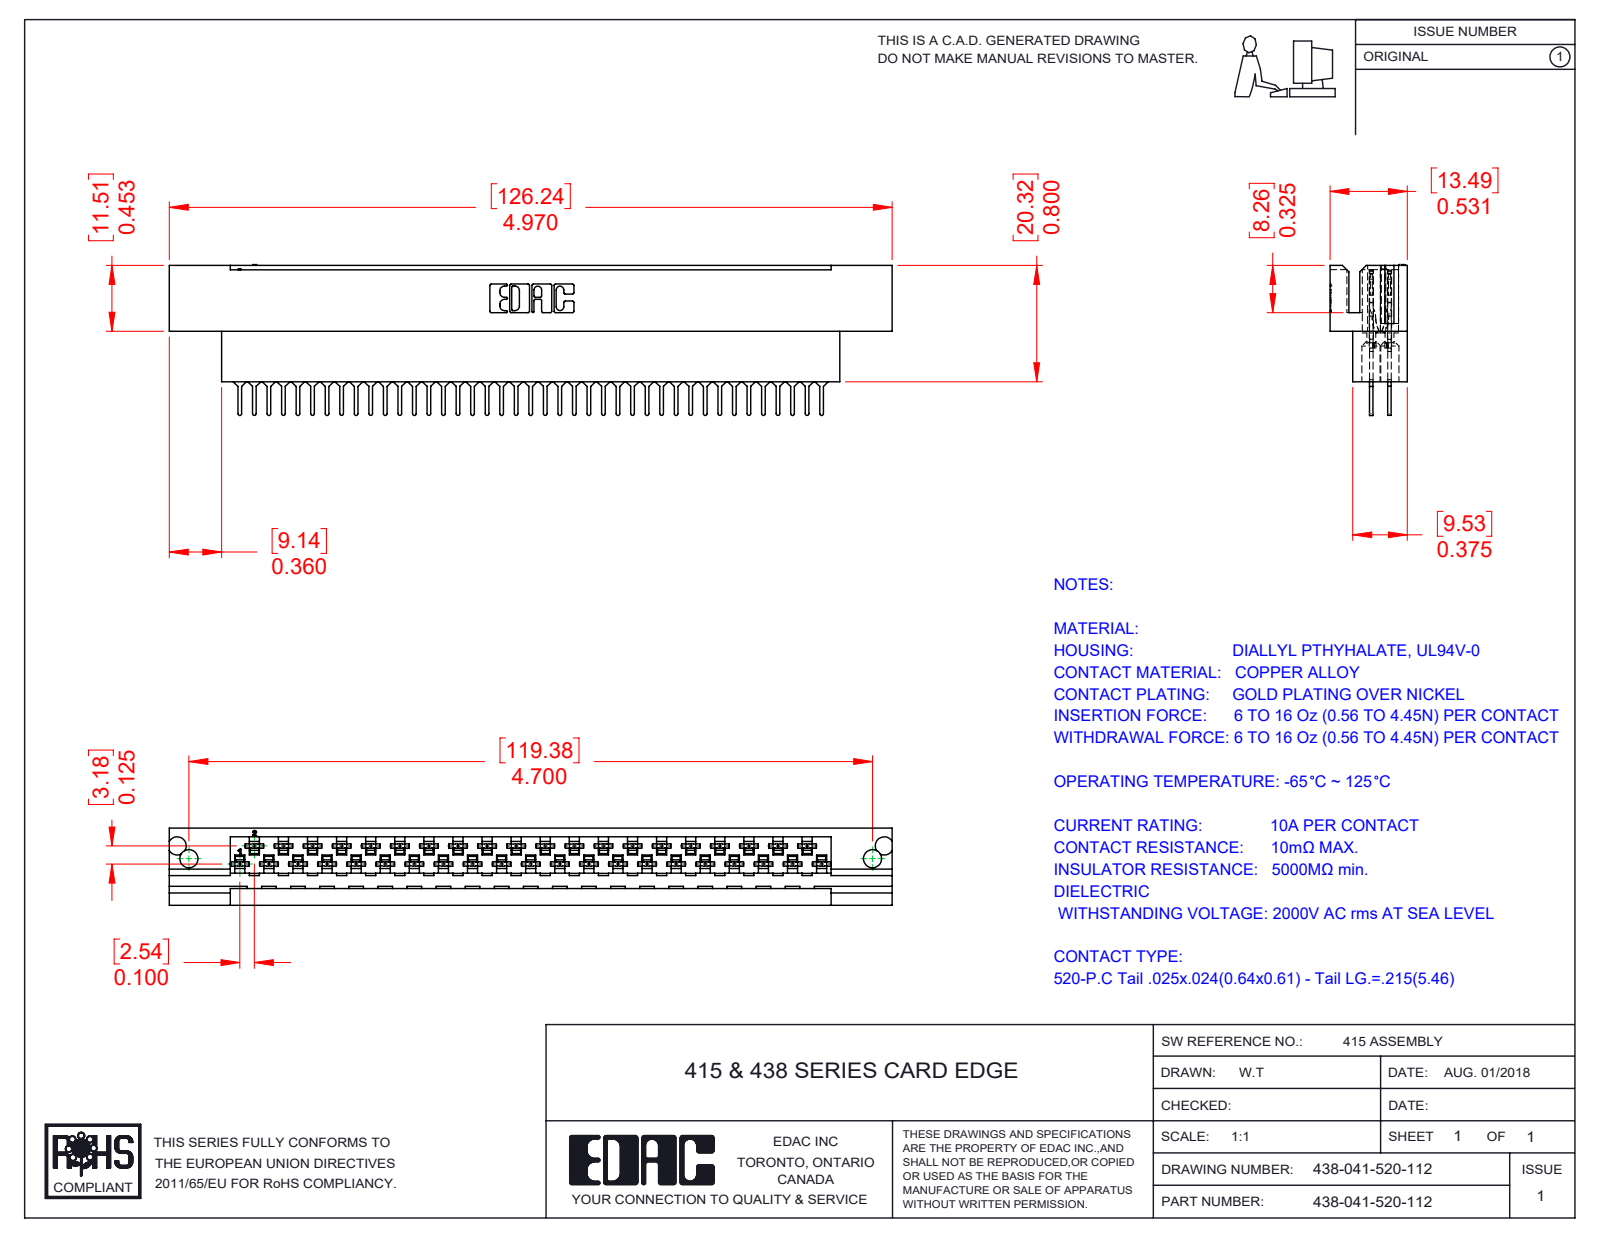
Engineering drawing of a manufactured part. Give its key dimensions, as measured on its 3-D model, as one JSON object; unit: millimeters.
{"part_name": "516-290-001_520; 438-210-001_438-210-041-112; 438-041-520-112", "step_written_by": "SolidWorks 2016 (CONFIG_CONTROL_DESIGN)", "units": "millimeters", "bodies": {"solids": 42, "faces": 4166, "planar": 2659, "cylindrical": 1116, "other": 391}, "overall_size": [126.24, 26.32, 13.49], "volume_mm3": 20937, "surface_area_mm2": 26218, "round_holes": [[1.27, 41], [3.3, 41], [3.17, 1], [3.18, 1]], "partial_cylinders_radius": [[0.3, 164], [0.56, 164], [0.18, 82], [0.2, 82], [0.41, 82], [2.03, 82], [0.32, 41], [0.25, 22]], "face_to_face_distances": [3.18, 1.88, 0.61, 1.27, 2.92, 3.96, 13.49, 7.49, 3.58, 6.61], "hole_center_spacings": [5.08, 10.16, 15.24, 20.32, 25.4, 30.48, 35.56, 2.54]}
